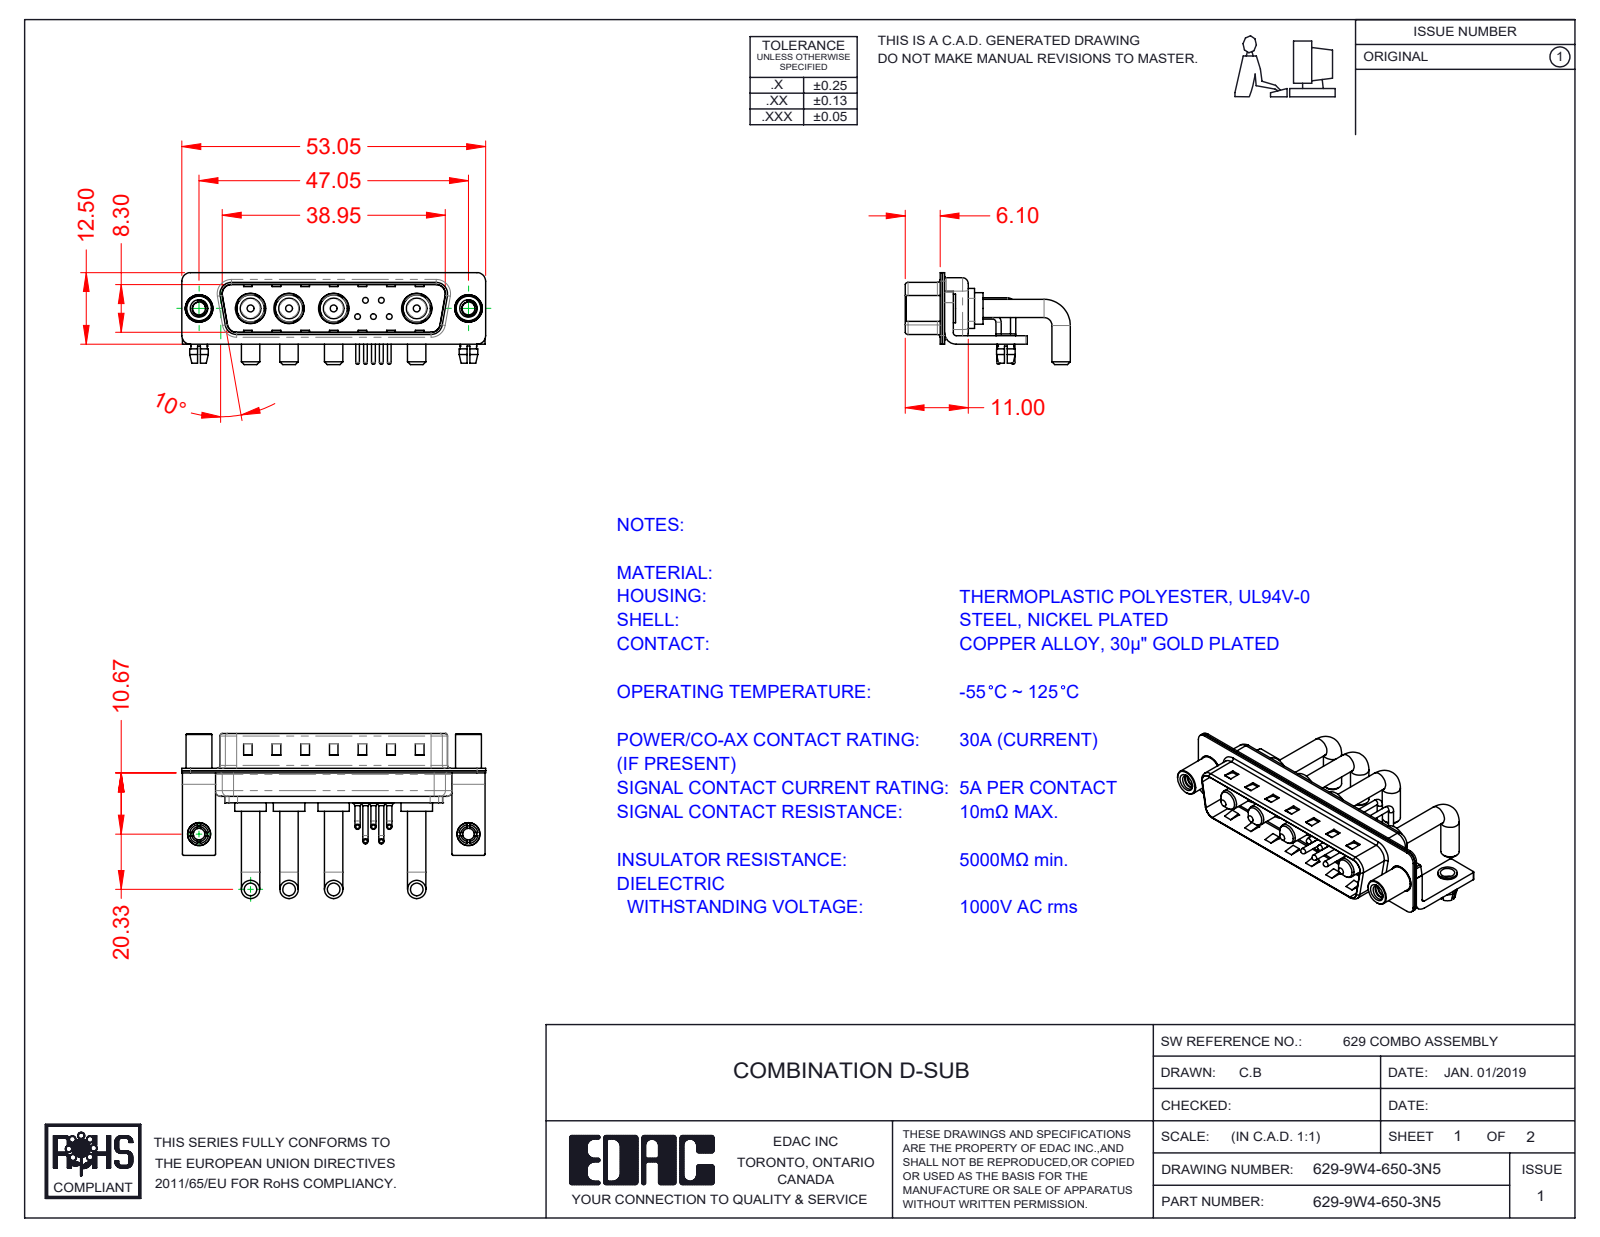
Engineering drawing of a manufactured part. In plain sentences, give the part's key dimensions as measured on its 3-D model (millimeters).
The part is named "629Combo Threaded Standoff_5; 629Combo Contact Row 1; 629Combo Shell Front_25 Contacts; 629Combo Stabilizer Bracket (+6 more)". Its 3-D file was written by "SolidWorks 2020 (CONFIG_CONTROL_DESIGN)". It is 22 solids with 1278 faces: 601 planar, 493 cylindrical and 184 other. Overall it measures 53.05 by 28.83 by 16.05 millimeters. Its volume is 4 079 cubic millimeters and its surface area 8 737 square millimeters. Round holes: 7 of diameter 2, 5 of diameter 0.75, 5 of diameter 1.6, 4 of diameter 4.85, 4 of diameter 5.3, 2 of diameter 2.26, 2 of diameter 2.5, 2 of diameter 3.2, 2 of diameter 4, 2 of diameter 4.8. Round bosses or shafts: 10 of diameter 0.9, 8 of diameter 3.2, 5 of diameter 1.5, 5 of diameter 1, 5 of diameter 0.65, 4 of diameter 5.5, 4 of diameter 5.2, 4 of diameter 4.75. Partial cylindrical surfaces (rounded edges, fillets, slot ends): 16 of radius 0.25, 16 of radius 1.5, 13 of radius 2, 9 of radius 0.5, 8 of radius 1.6, 5 of radius 1.01, 4 of radius 0.6, 4 of radius 0.65. The main face-to-face distances are 0.4, 0.8, 9.5, 1.5, 9.1, 8.7, 9.9, 5.2, 0.75, 1.2. The hole center spacings are 3.16, 2.77, 5.04, 14.5, 47.05, 2.78, 4.4, 4.41.
